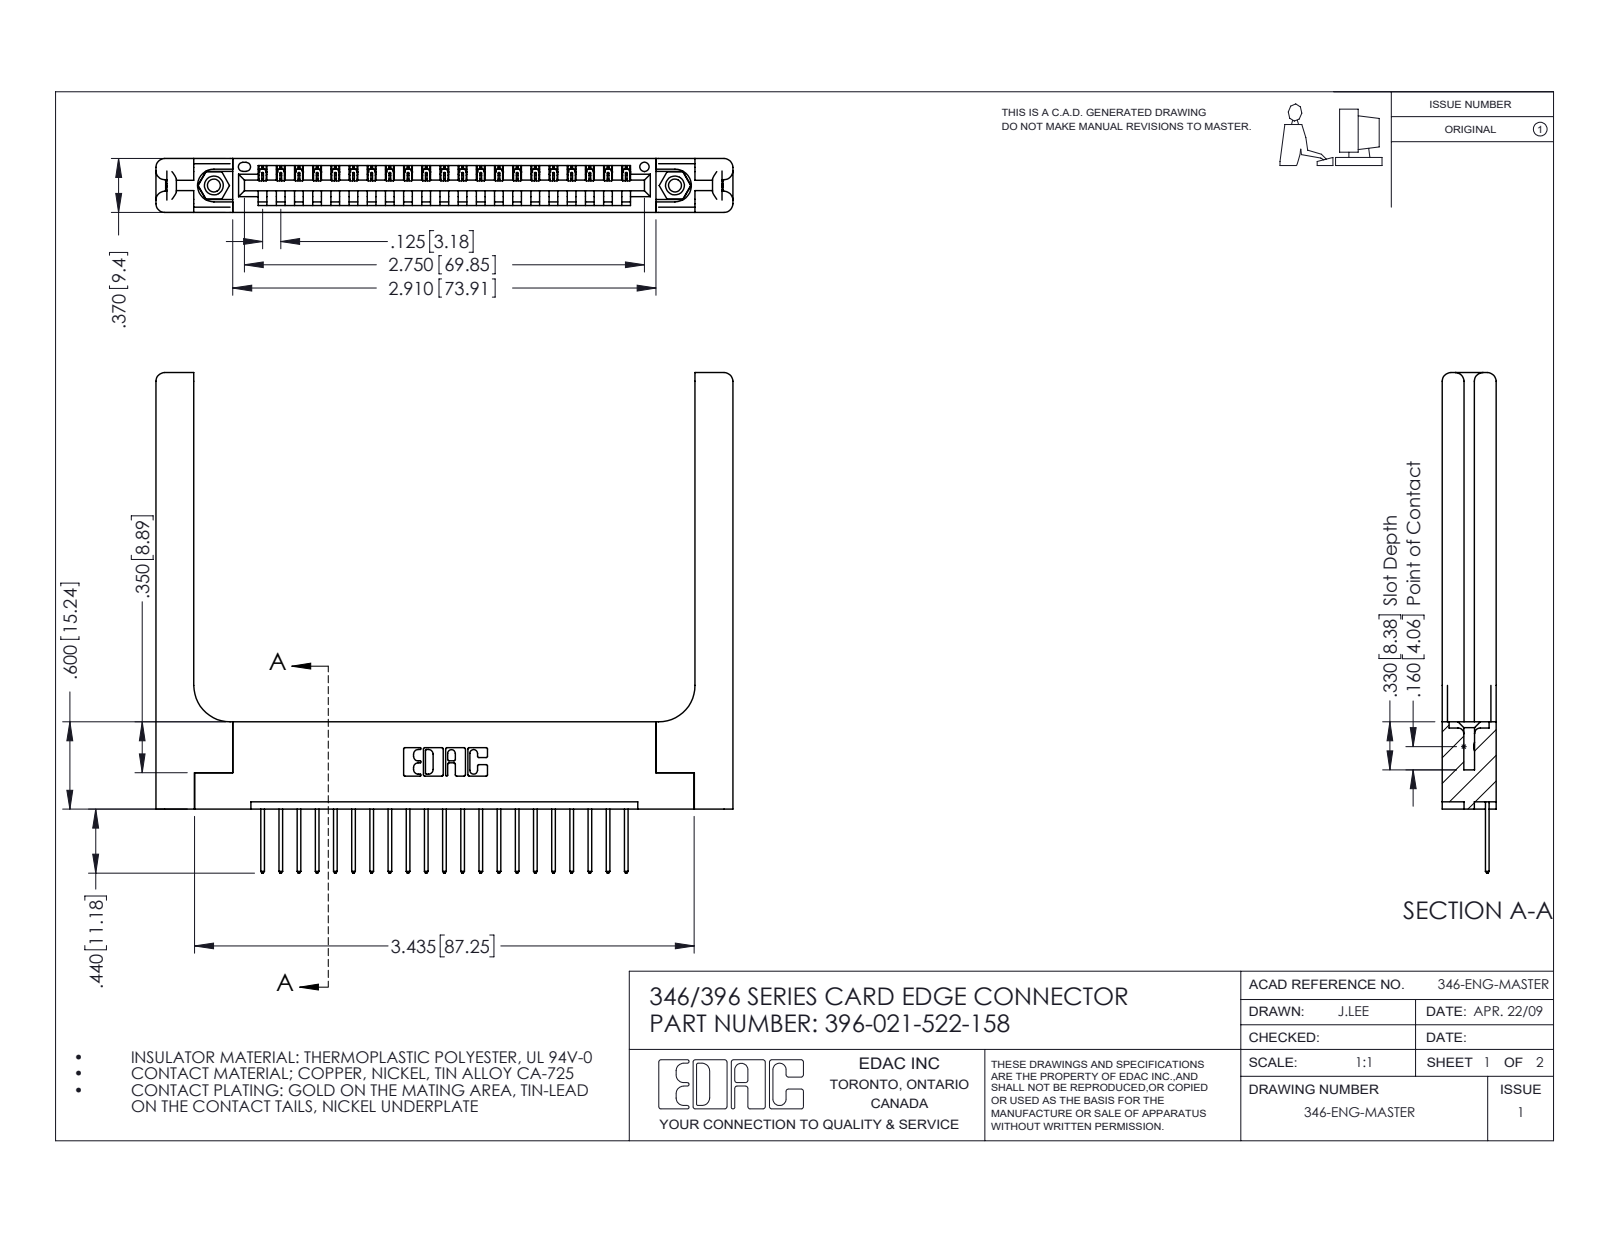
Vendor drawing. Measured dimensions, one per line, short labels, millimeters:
name: 396-021-522-158; 345-250-001_345-250-001-102; 346-220-058_345-220-058; 345-292-001_345-293-122 (+1 more)
written by: SolidWorks 2016 (CONFIG_CONTROL_DESIGN)
unit: mm
bodies: 26 solids, 1596 faces (1064 planar, 472 cylindrical, 60 other)
size: 100.7 × 87.4 × 9.4
volume: 17 030 mm³; area: 16 900 mm²
holes: 2× ⌀2.3, 2× ⌀3.2, 2× ⌀4, 1× ⌀1.6
bosses: 2× ⌀3.9
rounds: 42× R0.2, 42× R0.3, 22× R0.3, 16× R1.5, 6× R0.2, 6× R0.8, 3× R0.7, 2× R0.8
face distances: 9.4, 1.8, 1.2, 8.2, 3.8, 3.8, 6.4, 7.6, 0.6, 2.6
hole spacings: 6.2, 75.3, 80.5
